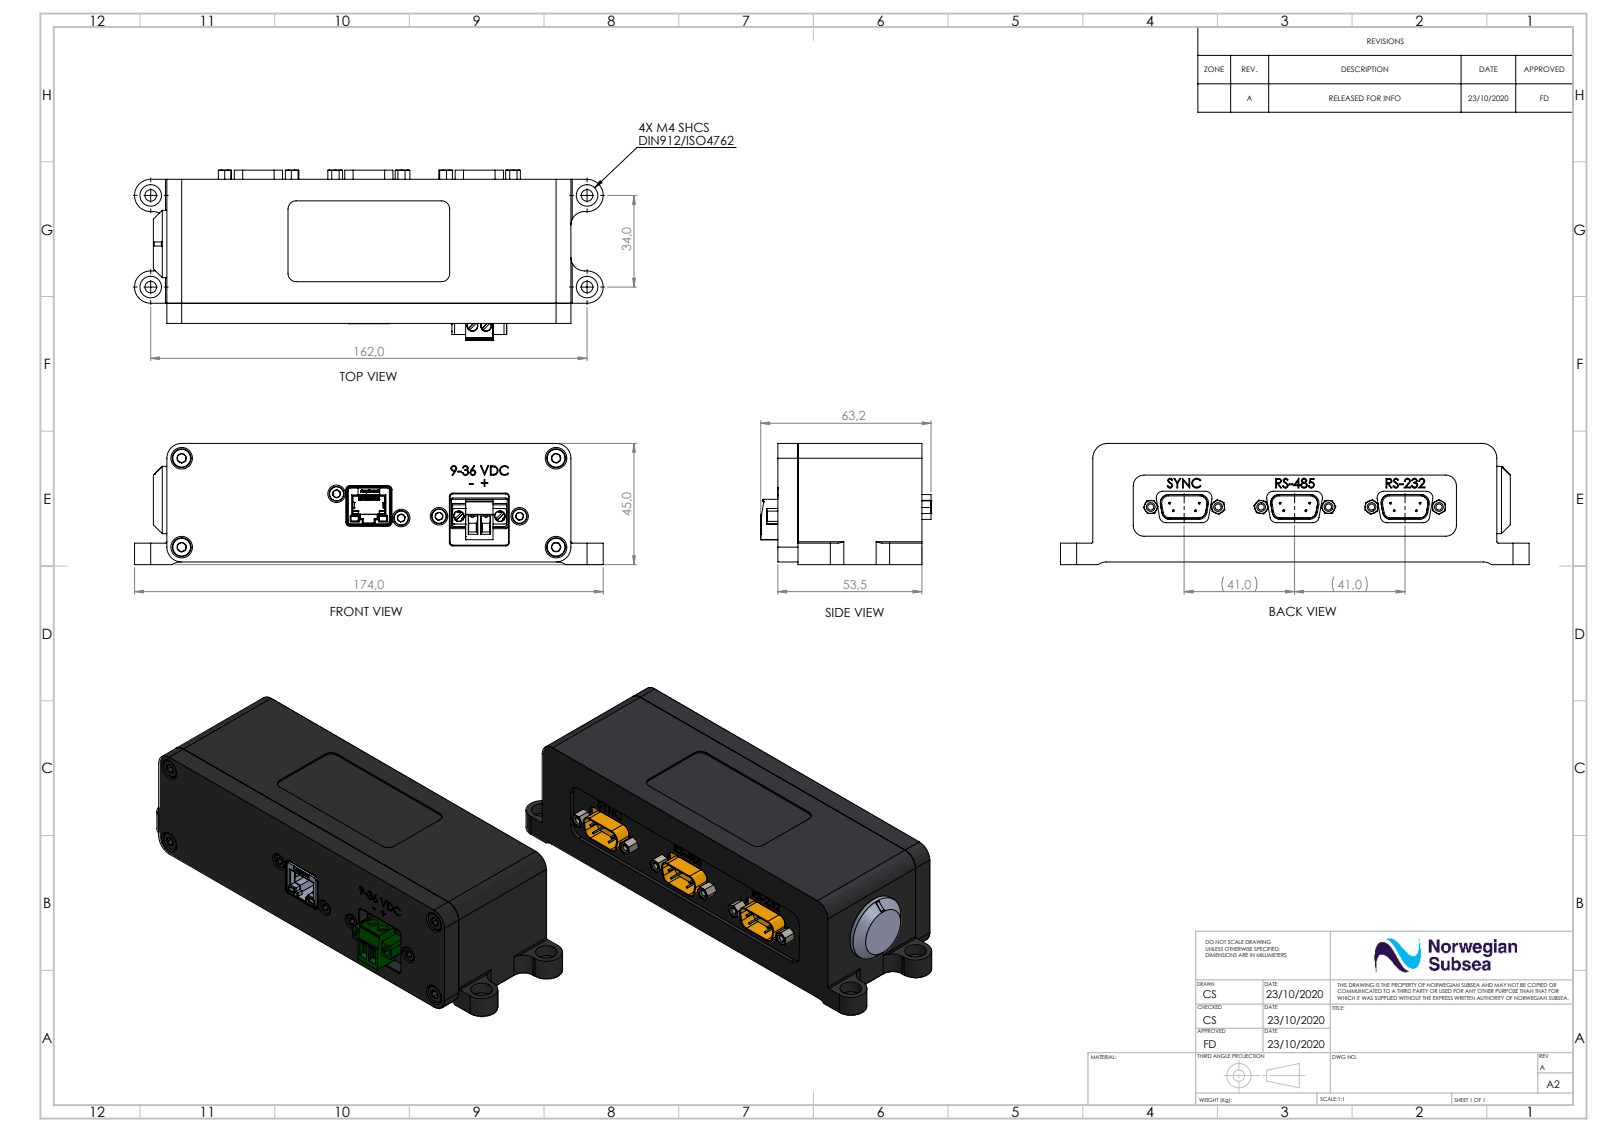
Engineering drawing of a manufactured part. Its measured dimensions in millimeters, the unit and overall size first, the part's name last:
Units: millimetres
Overall size (bounding box): 174 × 63.22 × 45
Round holes (diameter × count): ⌀1 ×27, ⌀0.41 ×26, ⌀3 ×14, ⌀0.9 ×12, ⌀3.2 ×11, ⌀3.3 ×10, ⌀2.26 ×8, ⌀2.5 ×8, ⌀8 ×8, ⌀1.4 ×4, ⌀4.3 ×4, ⌀4.5 ×4
Round bosses / shafts (diameter × count): ⌀0.4 ×52, ⌀0.6 ×24, ⌀5.5 ×7, ⌀3 ×7, ⌀2.35 ×7, ⌀2.85 ×6, ⌀7 ×4, ⌀4 ×4
Partial cylindrical surfaces — rounded edges, fillets, slot ends (radius × count): R0.1 ×104, R1 ×46, R0.13 ×32, R0.25 ×31, R0.5 ×24, R0.3 ×20, R0.75 ×20, R0.21 ×17
Main face-to-face distances: 3, 41, 32.5, 38, 44, 8.5, 27.91, 13.09, 10.09, 30.91
Hole centre spacings: 2.89, 41, 2.74, 4.83, 5.48, 5.08, 7.31, 25
Volume: 180 054 mm³ · Surface area: 116 323 mm²
Bodies: 63 solids, 8126 faces (1894 planar, 2244 cylindrical, 3988 other)
Part name (STEP PRODUCT): M3 Spacer DIA 4.5x4_94669A097; pxc_1898981_05_DFK-MSTBA-2-5-2-GF-5-08_3D; B1; LEMO-4 (+8 more)
STEP written by: SolidWorks 2020 (AUTOMOTIVE_DESIGN)
